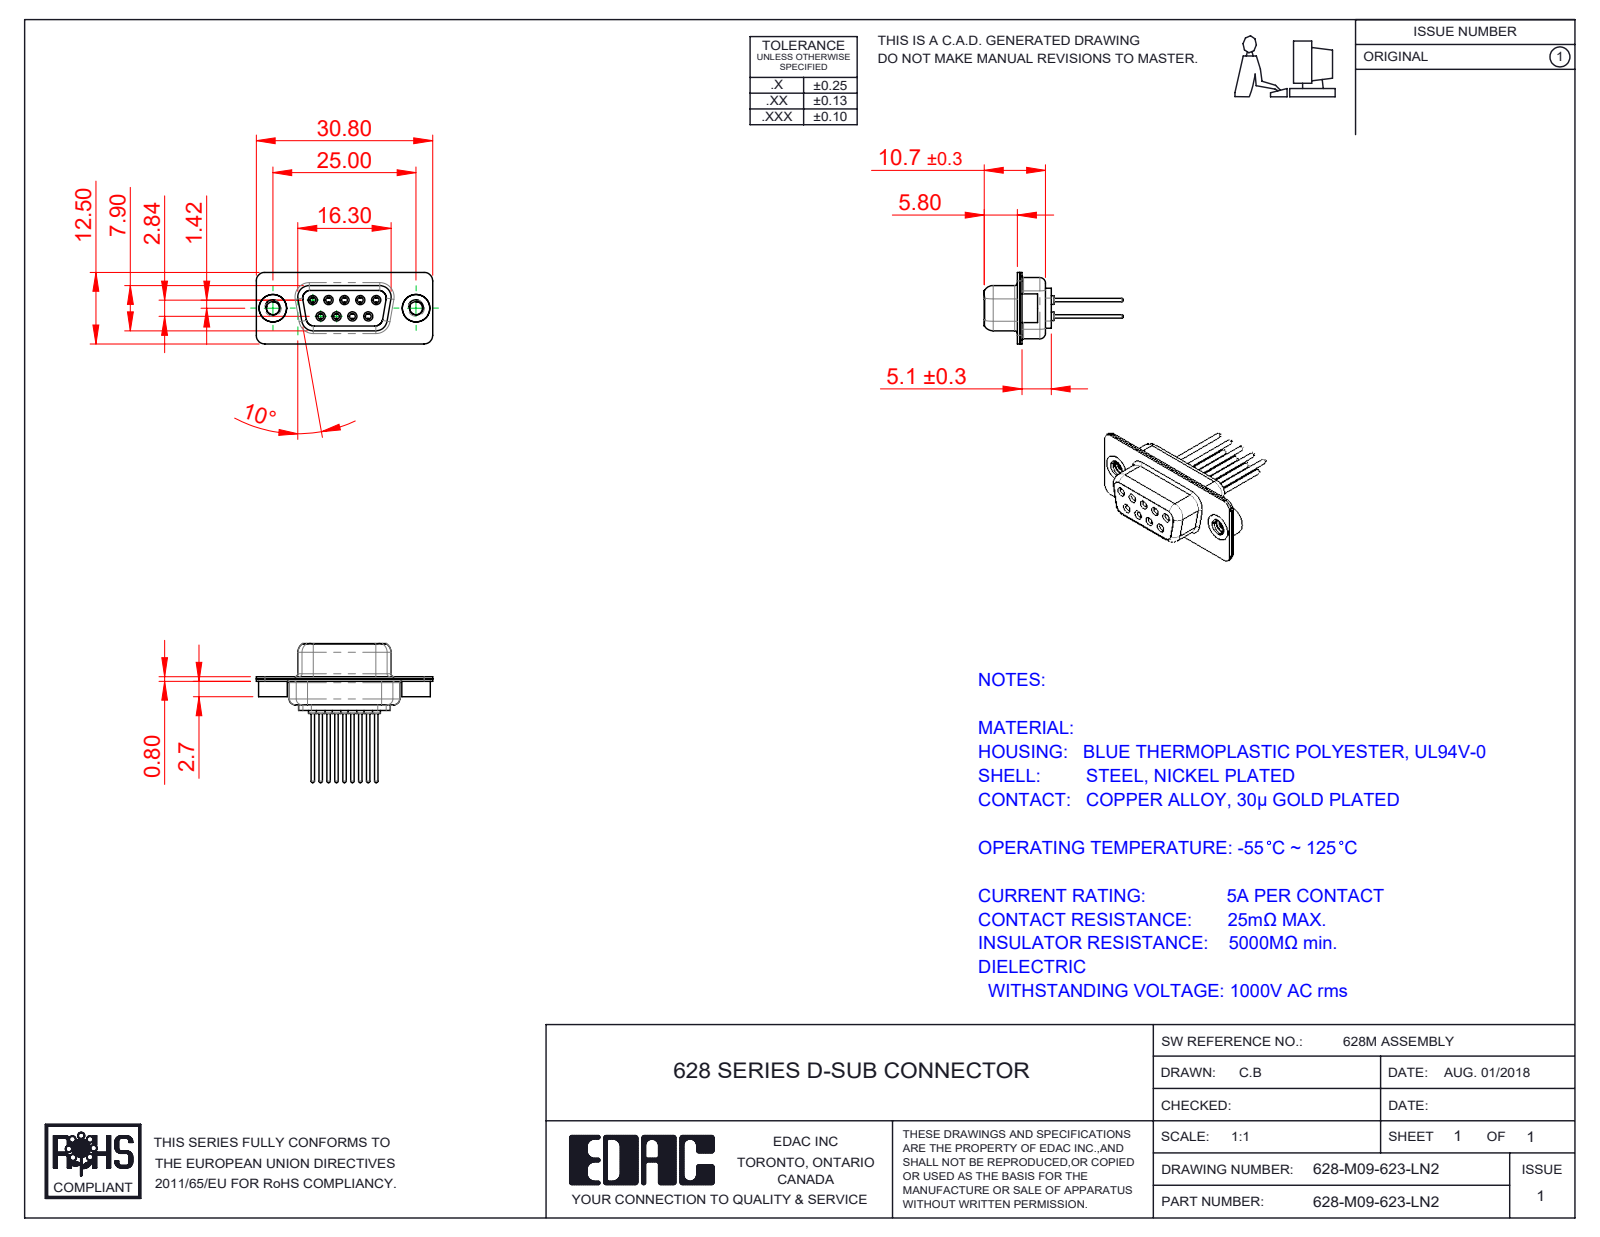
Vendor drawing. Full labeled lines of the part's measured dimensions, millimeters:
Part name (STEP PRODUCT): 628M Housing_09 Contacts; 628M 4-40 Threaded Rivet; 628-M09-623-LN2; 628M Contact Row 2_23 (+3 more)
STEP written by: SolidWorks 2020 (CONFIG_CONTROL_DESIGN)
Units: millimetres
Bodies: 14 solids, 774 faces (202 planar, 308 cylindrical, 264 other)
Overall size (bounding box): 30.8 × 24.27 × 12.5
Volume: 1 721 mm³ · Surface area: 4 540 mm²
Round holes (diameter × count): ⌀1 ×9, ⌀1.1 ×9, ⌀1.7 ×9, ⌀1.8 ×9, ⌀2 ×9, ⌀2.26 ×2, ⌀4 ×2, ⌀4.8 ×2
Round bosses / shafts (diameter × count): ⌀2.2 ×9, ⌀1.6 ×9, ⌀1.5 ×9, ⌀0.6 ×9, ⌀5 ×2, ⌀4.9 ×2
Partial cylindrical surfaces — rounded edges, fillets, slot ends (radius × count): R1.5 ×16, R2 ×12, R1.35 ×8, R1.6 ×8, R0.25 ×4, R0.5 ×4, R0.6 ×4, R0.65 ×4
Main face-to-face distances: 0.4, 1.4, 0.45, 8.45, 0.8, 1, 8.9, 1.8, 6.2, 7.05
Hole centre spacings: 3.16, 2.77, 5.54, 5.03, 5.04, 8.31, 7.1, 7.48
